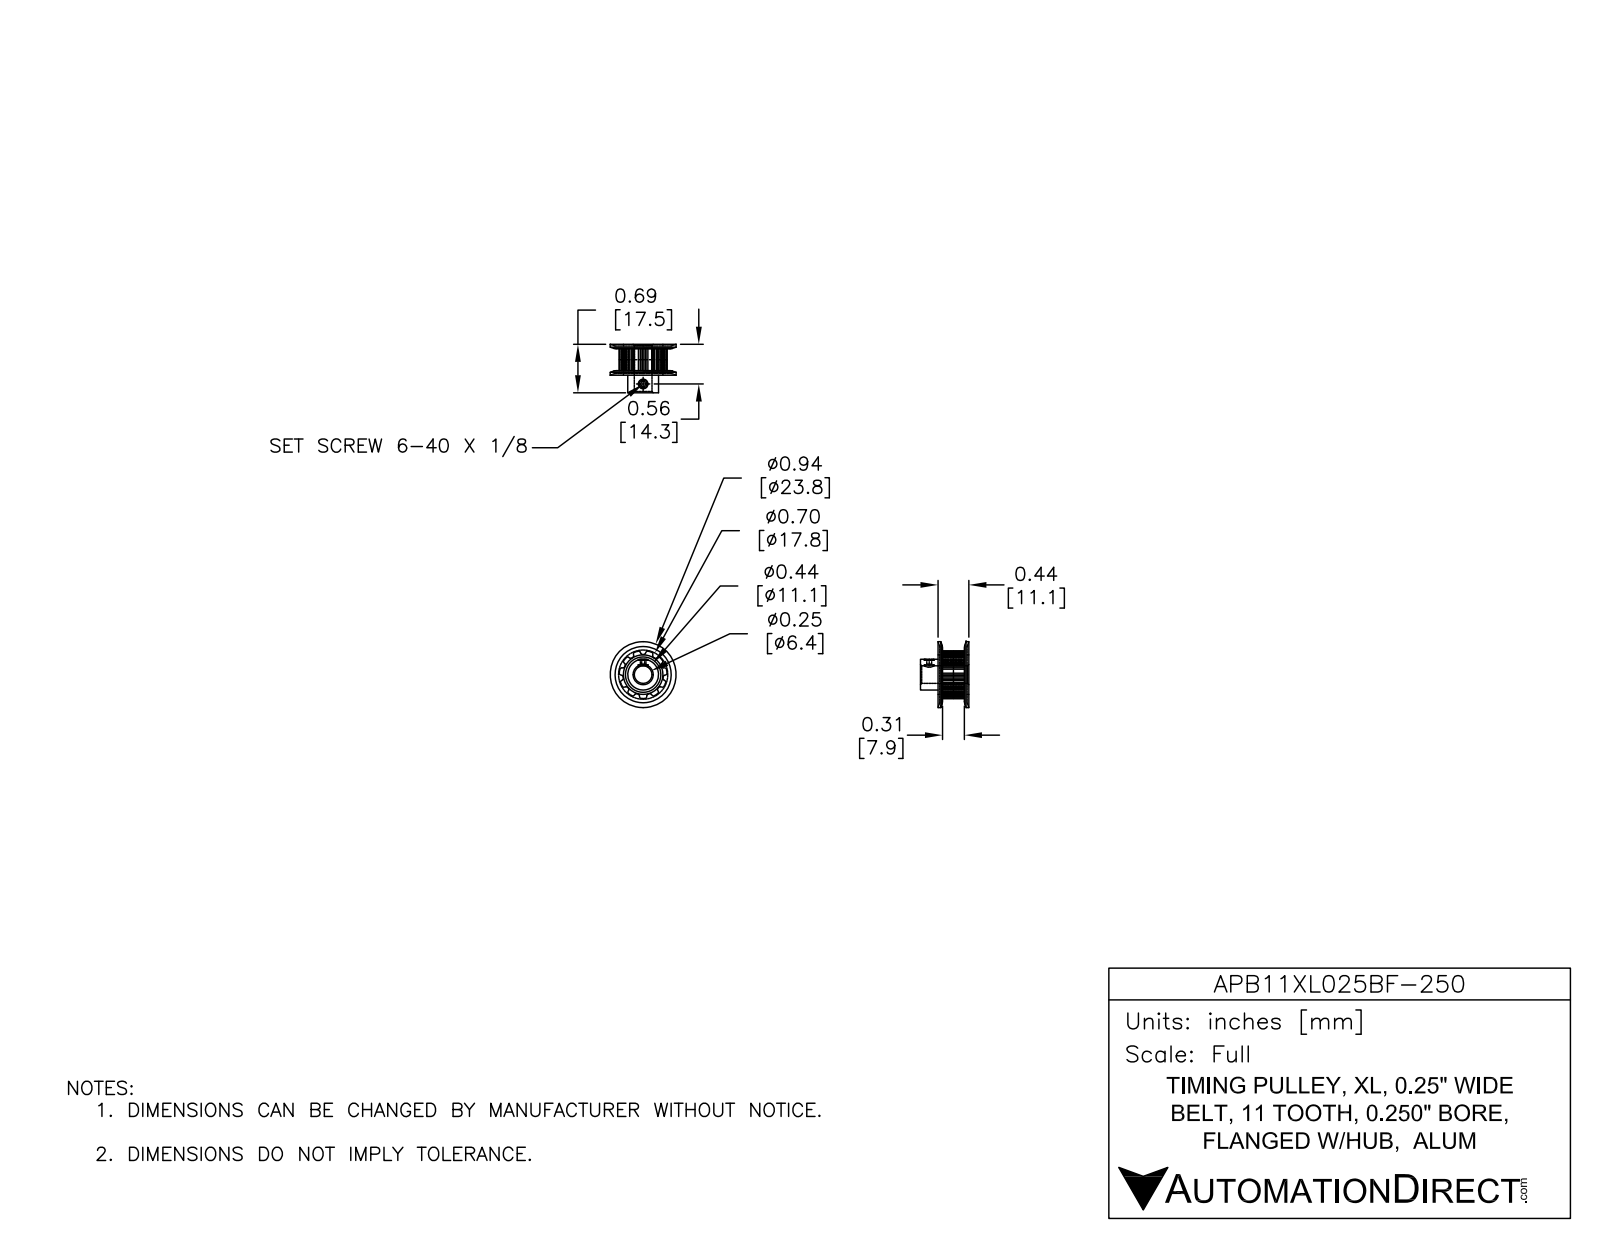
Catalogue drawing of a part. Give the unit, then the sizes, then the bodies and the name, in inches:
Units: inches
Overall size (bounding box): 0.938 × 0.938 × 0.688
Round holes (diameter × count): ⌀0.088 ×2, ⌀0.25 ×1
Round bosses / shafts (diameter × count): ⌀0.438 ×1
Partial cylindrical surfaces — rounded edges, fillets, slot ends (radius × count): R0.015 ×44, R0.285 ×1
Main face-to-face distances: 0.375, 0.033, 0.407, 0.688, 0.656, 0.281, 0.342, 0.313, 0.065, 0.032
Volume: 0.155 in³ · Surface area: 4.039 in²
Bodies: 1 solid, 134 faces (39 planar, 73 cylindrical, 22 other)
Part name (STEP PRODUCT): APB11XL025BF-250
STEP written by: SolidWorks 2014 (AUTOMOTIVE_DESIGN)
